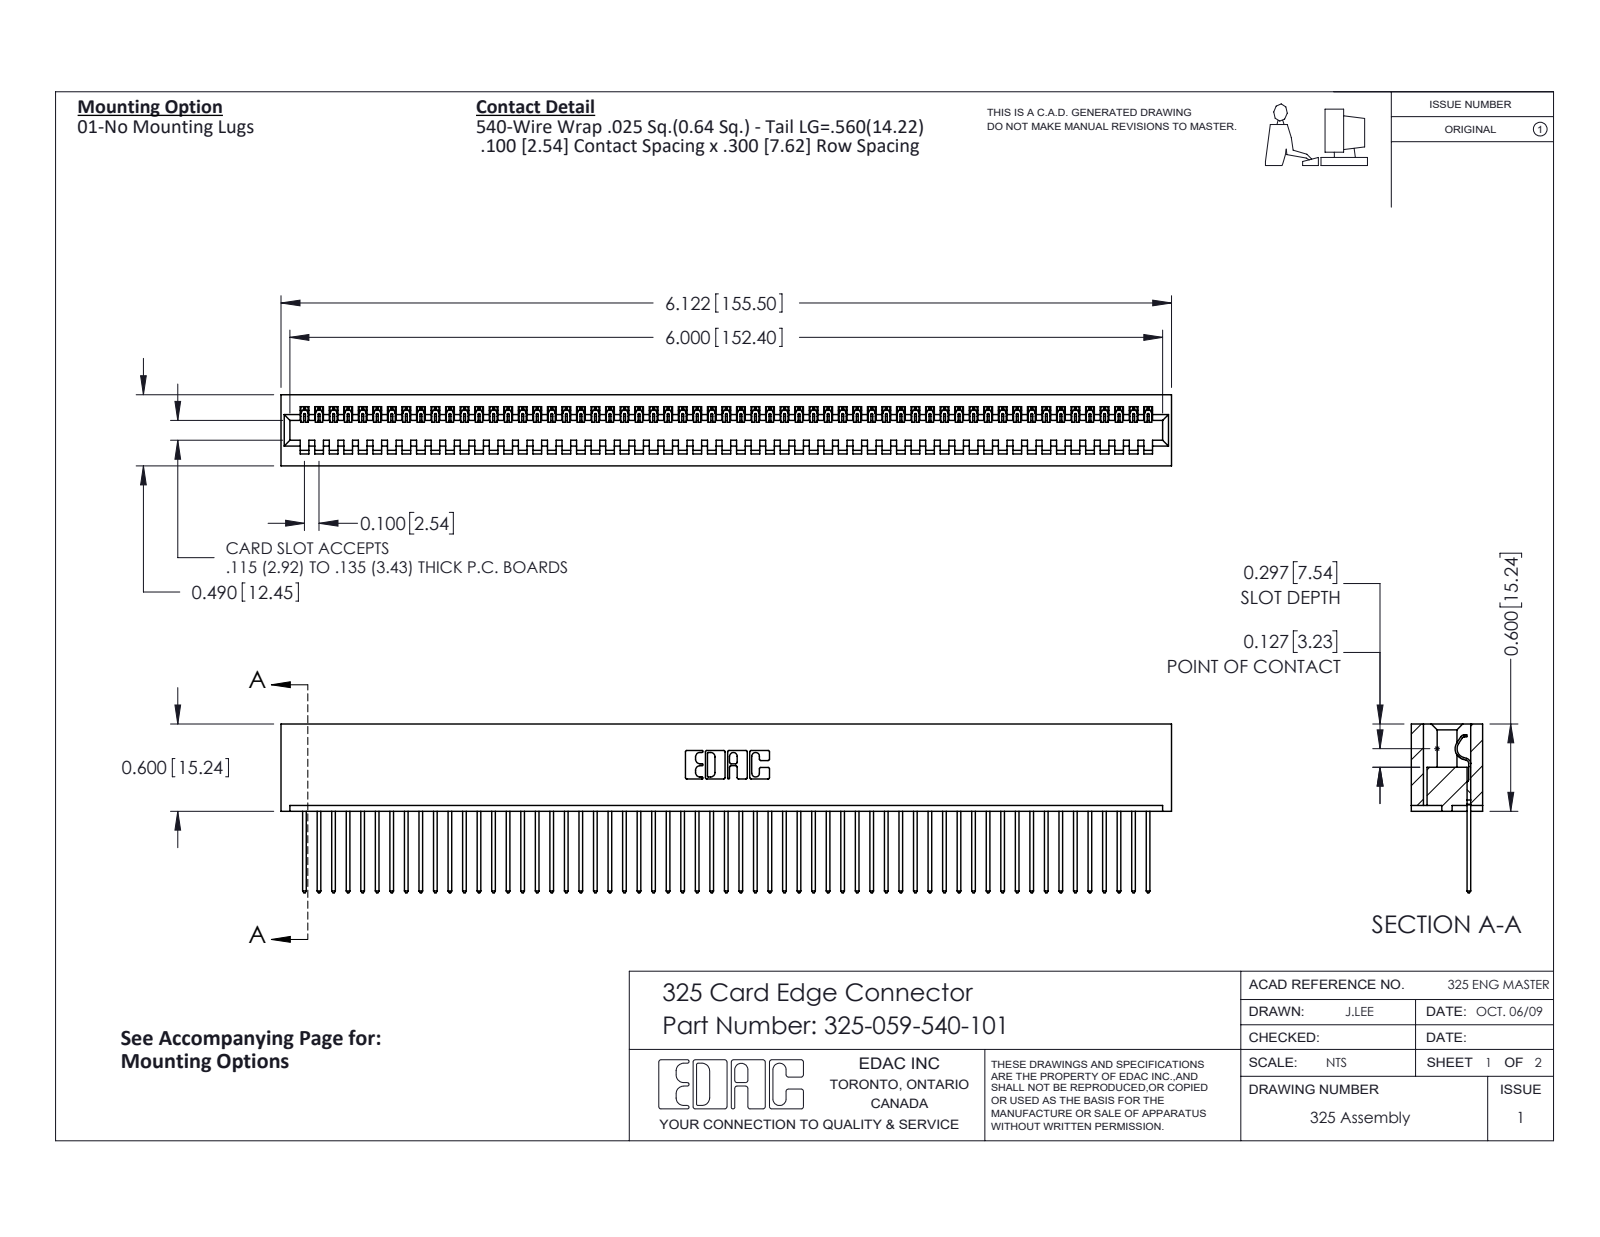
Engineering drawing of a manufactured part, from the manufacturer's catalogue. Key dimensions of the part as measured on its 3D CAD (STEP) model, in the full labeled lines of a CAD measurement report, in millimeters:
Part name (STEP PRODUCT): 325-292-001_325-293-140; 325 Part_Lugless; 325-059-540-101
STEP written by: SolidWorks 2016 (CONFIG_CONTROL_DESIGN)
Units: millimetres
Bodies: 60 solids, 3528 faces (2544 planar, 984 cylindrical, 0 other)
Overall size (bounding box): 155.5 × 29.5 × 12.4
Volume: 20 530 mm³ · Surface area: 23 790 mm²
Partial cylindrical surfaces — rounded edges, fillets, slot ends (radius × count): R0.2 ×118, R0.3 ×118, R0.3 ×22, R0.2 ×6, R0.8 ×6, R0.7 ×3, R0.4 ×1, R0.6 ×1
Main face-to-face distances: 2.1, 10.3, 7.6, 12.4, 2.7, 9.7, 0.6, 8.3, 14.2, 6.7
